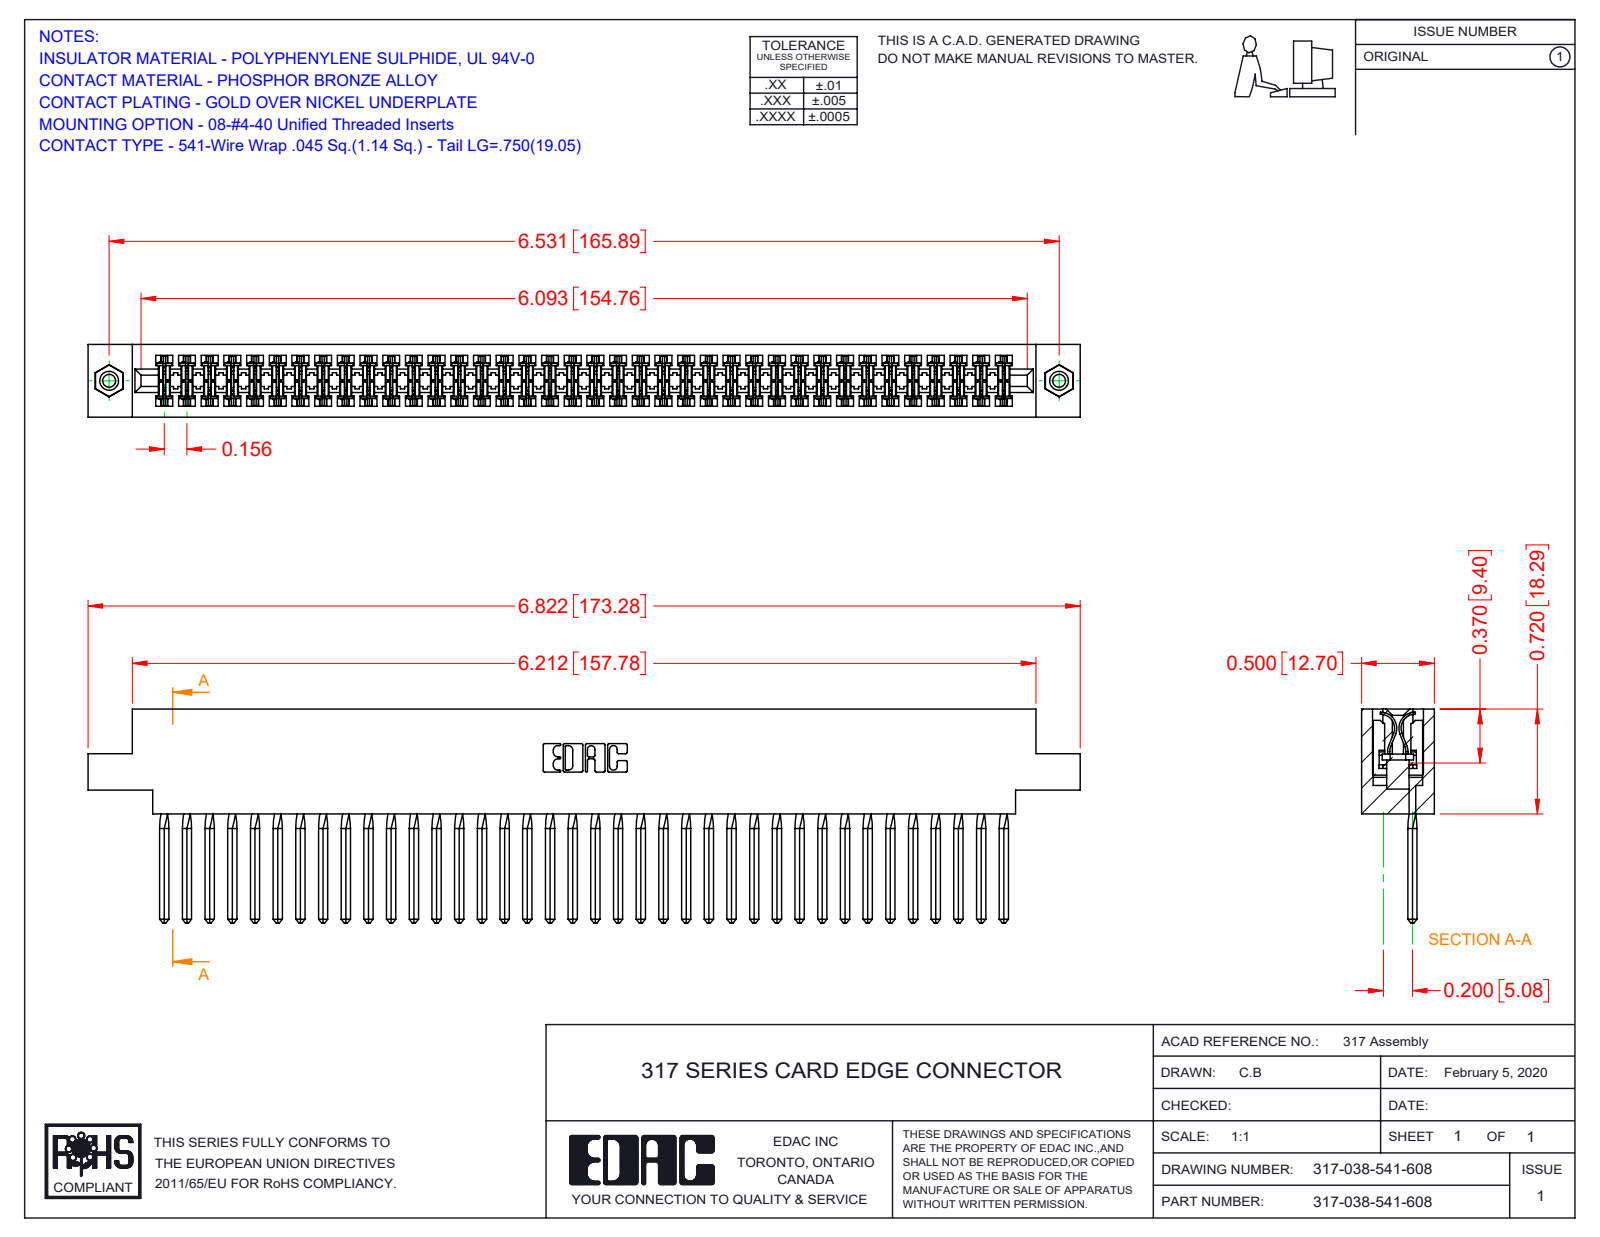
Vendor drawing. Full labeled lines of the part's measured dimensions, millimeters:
Part name (STEP PRODUCT): 317-038-541-608; 317 Part_.156 Dia - TI; 317-290-002_541; 345-250-001_345-250-003-102
STEP written by: SolidWorks 2016 (CONFIG_CONTROL_DESIGN)
Units: millimetres
Bodies: 41 solids, 5938 faces (4802 planar, 968 cylindrical, 168 other)
Overall size (bounding box): 173.3 × 37.3 × 12.7
Volume: 27 970 mm³ · Surface area: 39 410 mm²
Round holes (diameter × count): ⌀2.3 ×2, ⌀3.2 ×2, ⌀4 ×2
Round bosses / shafts (diameter × count): ⌀3.9 ×2
Partial cylindrical surfaces — rounded edges, fillets, slot ends (radius × count): R0.4 ×76, R0.3 ×22, R0.2 ×6, R0.8 ×6, R0.7 ×3, R2.4 ×2, R2.5 ×2, R2.8 ×2
Main face-to-face distances: 12.7, 1.9, 10.8, 8.9, 5, 2.8, 18.3, 2.9, 3.5, 5.4
Hole centre spacings: 165.9
